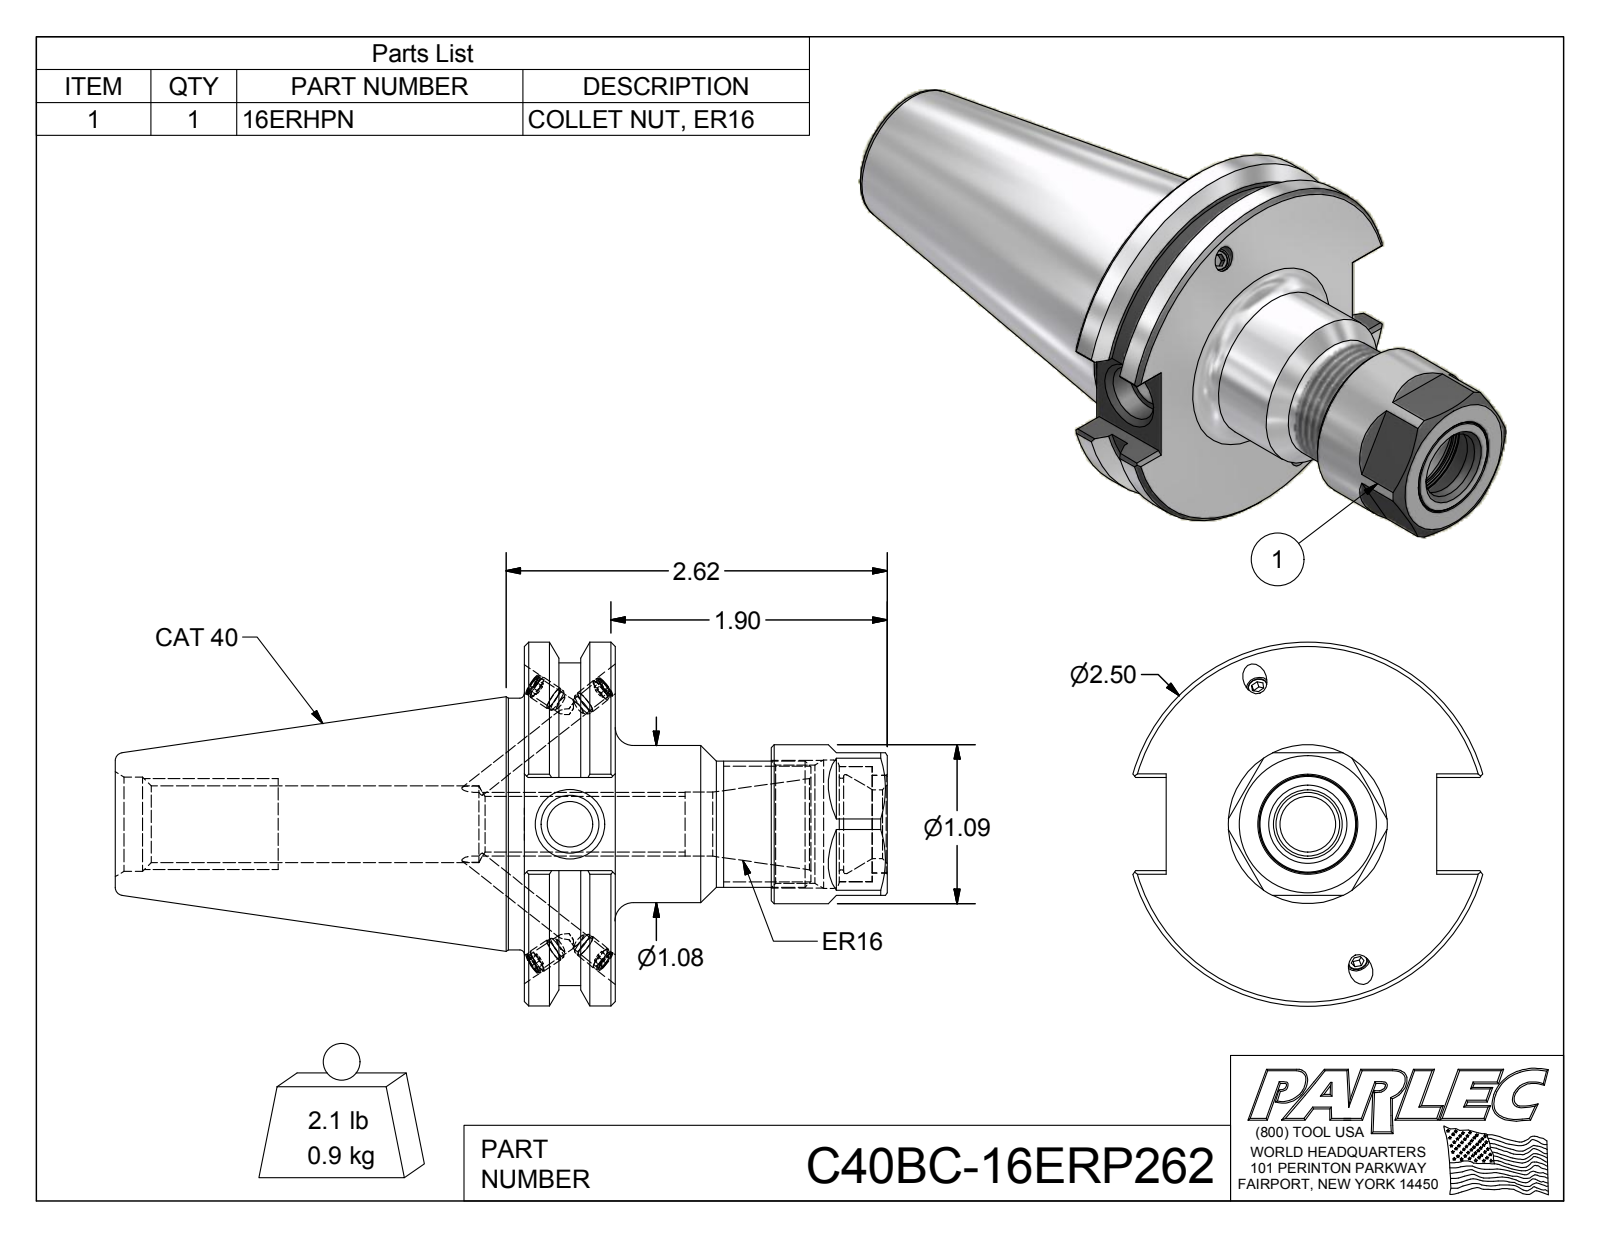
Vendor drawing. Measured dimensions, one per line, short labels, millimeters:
name: C40BC-16ERP262; C40BCB-16ER2-1; 029-965; 16ERHPN
written by: Autodesk Inventor 2012 (AUTOMOTIVE_DESIGN)
unit: mm
bodies: 7 solids, 192 faces (96 planar, 45 cylindrical, 51 other)
size: 134.8 × 63.5 × 61
volume: 120 100 mm³; area: 29 700 mm²
holes: 4× ⌀3.3, 4× ⌀4.1, 1× ⌀8, 1× ⌀9.7, 1× ⌀10.1, 1× ⌀11.2, 1× ⌀12, 1× ⌀13.4, 1× ⌀16, 1× ⌀16.5, 1× ⌀17.1, 1× ⌀17.3
bosses: 4× ⌀4.2, 4× ⌀4, 1× ⌀63.5, 1× ⌀56.4, 1× ⌀43.9, 1× ⌀27.7, 1× ⌀27.4, 1× ⌀22
face distances: 15.9, 24.9, 63.4, 47.5, 4.3, 20.6, 43.2, 27.3, 20.2, 16.3
